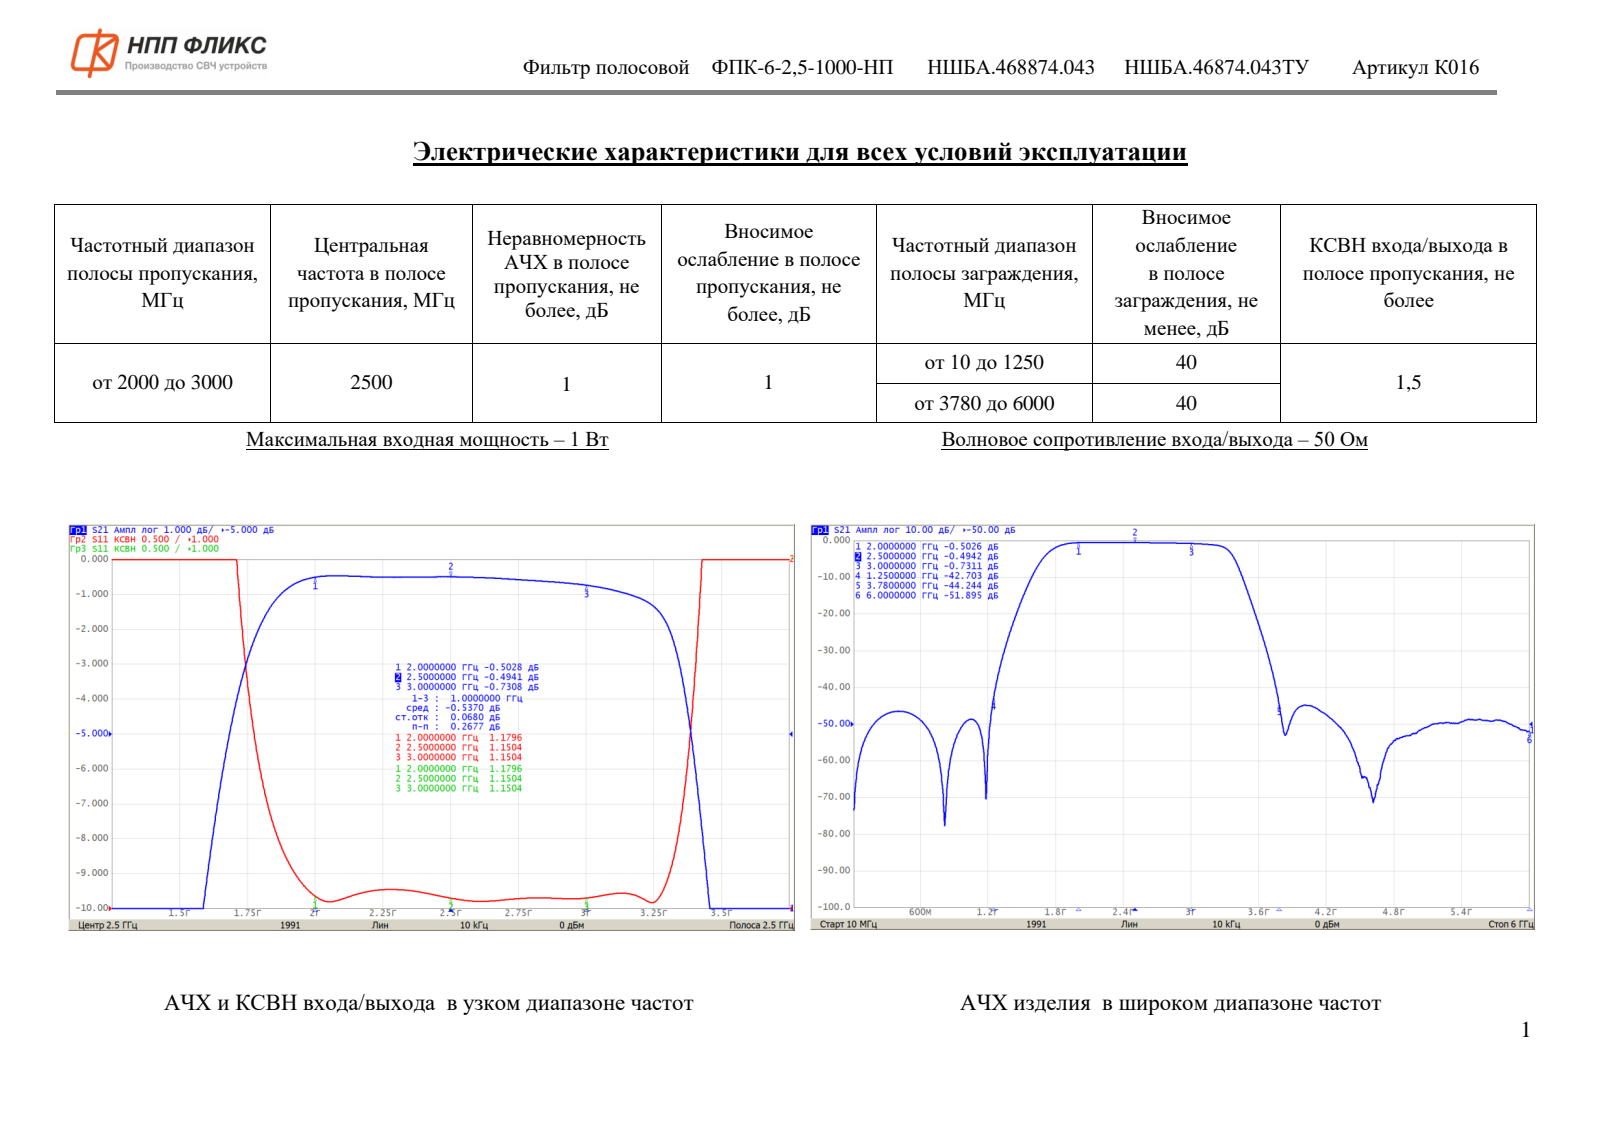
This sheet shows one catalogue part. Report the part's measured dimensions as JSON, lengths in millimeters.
{"part_name": "НШБА.468874.043_Фильтр ФПК-6-2,5-1000-НП", "step_written_by": "ASCON Math Kernel (CONFIG_CONTROL_DESIGN)", "units": "millimeters", "bodies": {"solids": 1, "faces": 709, "planar": 425, "cylindrical": 140, "other": 144}, "overall_size": [28, 20, 6.71], "volume_mm3": 427, "surface_area_mm2": 2744, "round_holes": [[0.5, 87], [2.2, 4], [0.8, 2]], "partial_cylinders_radius": [[0.4, 11], [0.2, 9], [0.3, 8], [1, 4], [0.6, 1], [0.7, 1]], "face_to_face_distances": [0.51, 6.51, 6, 6.2, 6.71, 17.7, 18.3, 17.5, 17.9, 0.4], "hole_center_spacings": [1.57, 2.8, 2.52, 1.4, 3.77, 3.13, 5.1, 3.96]}
